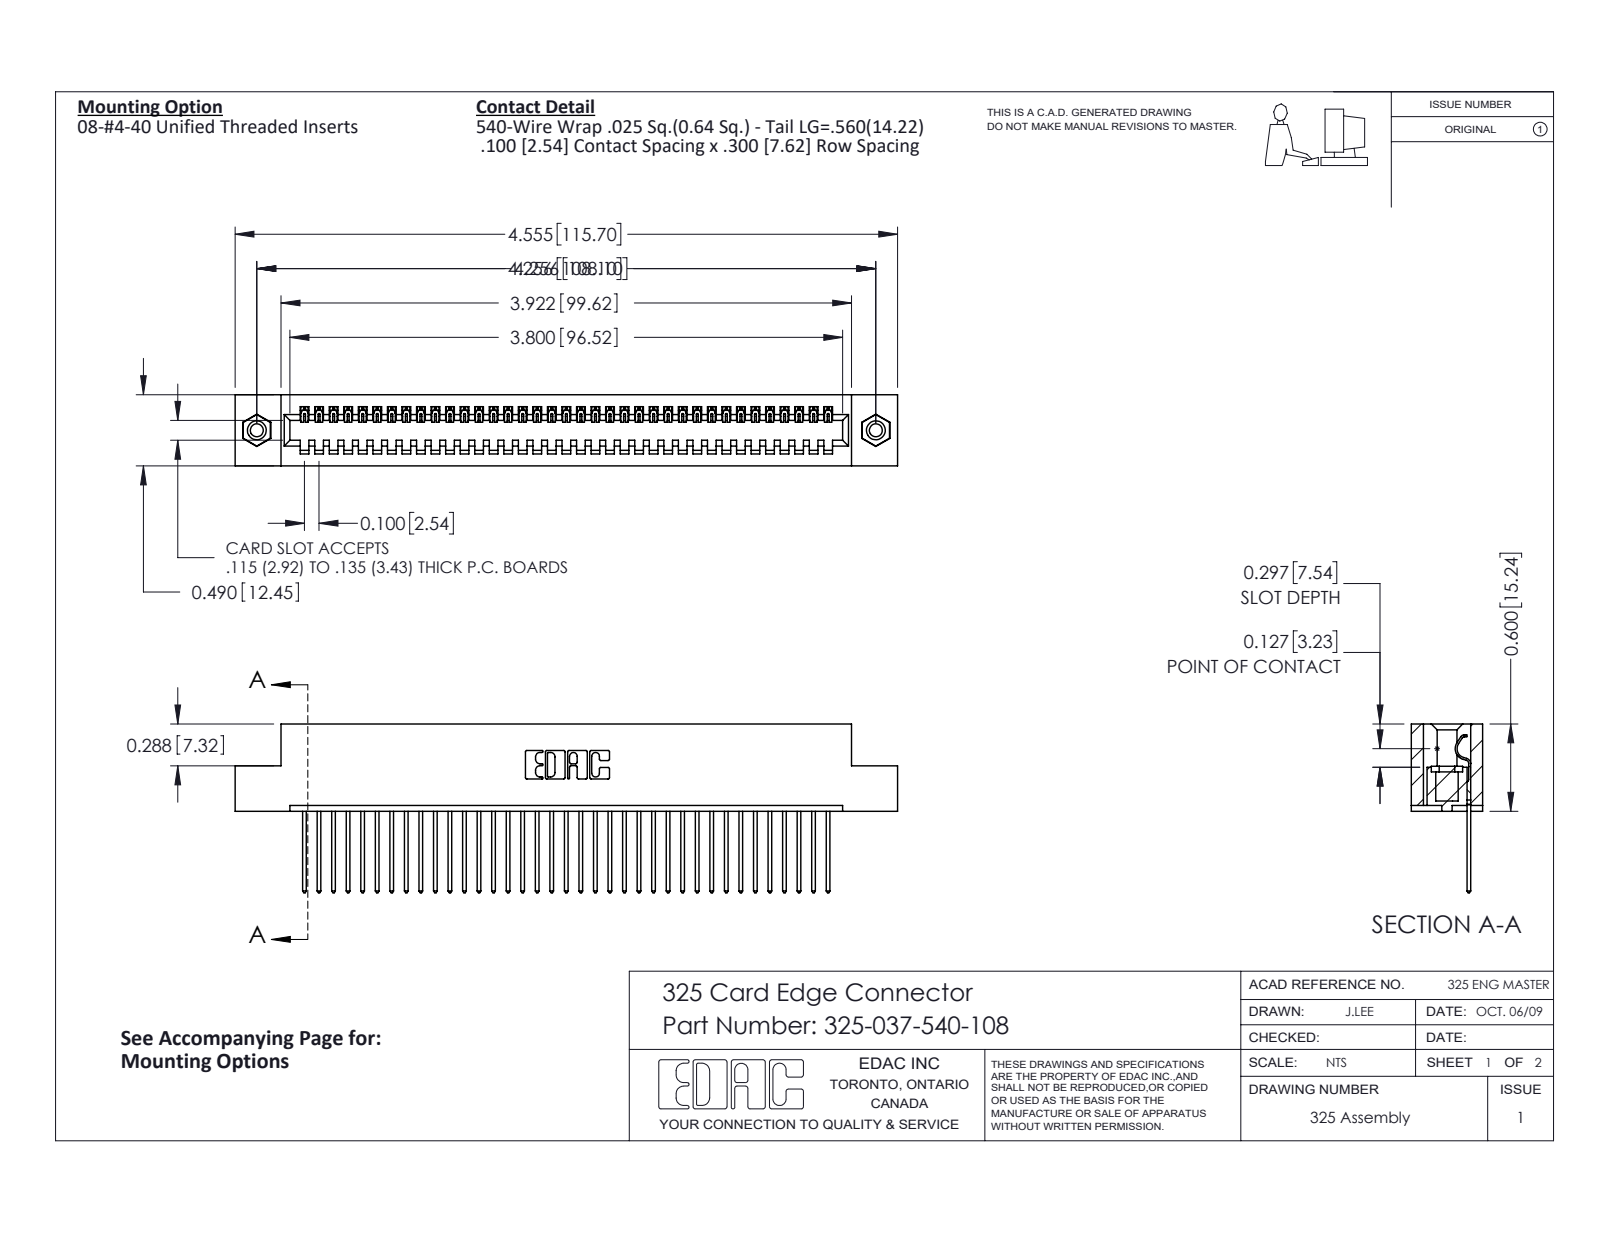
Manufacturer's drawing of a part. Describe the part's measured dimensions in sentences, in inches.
The part is named "325-037-540-108; 325 Part_TI; 345-250-001_345-250-003-102; 325-292-001_325-293-140". Its 3-D file was written by "SolidWorks 2016 (CONFIG_CONTROL_DESIGN)". It is 40 solids with 2320 faces: 1656 planar, 648 cylindrical and 16 other. Overall it measures 4.555 by 1.16 by 0.49 inches. Its volume is 0.897 cubic inches and its surface area 25.35 square inches. Round holes: 2 of diameter 0.089, 2 of diameter 0.125, 2 of diameter 0.16. Round bosses or shafts: 2 of diameter 0.155. Partial cylindrical surfaces (rounded edges, fillets, slot ends): 74 of radius 0.006, 74 of radius 0.01, 22 of radius 0.01, 6 of radius 0.007, 6 of radius 0.031, 3 of radius 0.026, 1 of radius 0.014, 1 of radius 0.022. The main face-to-face distances are 0.083, 0.407, 0.49, 0.3, 0.107, 0.383, 0.025, 0.325, 0.56, 0.263. The hole center spacings are 4.256.
